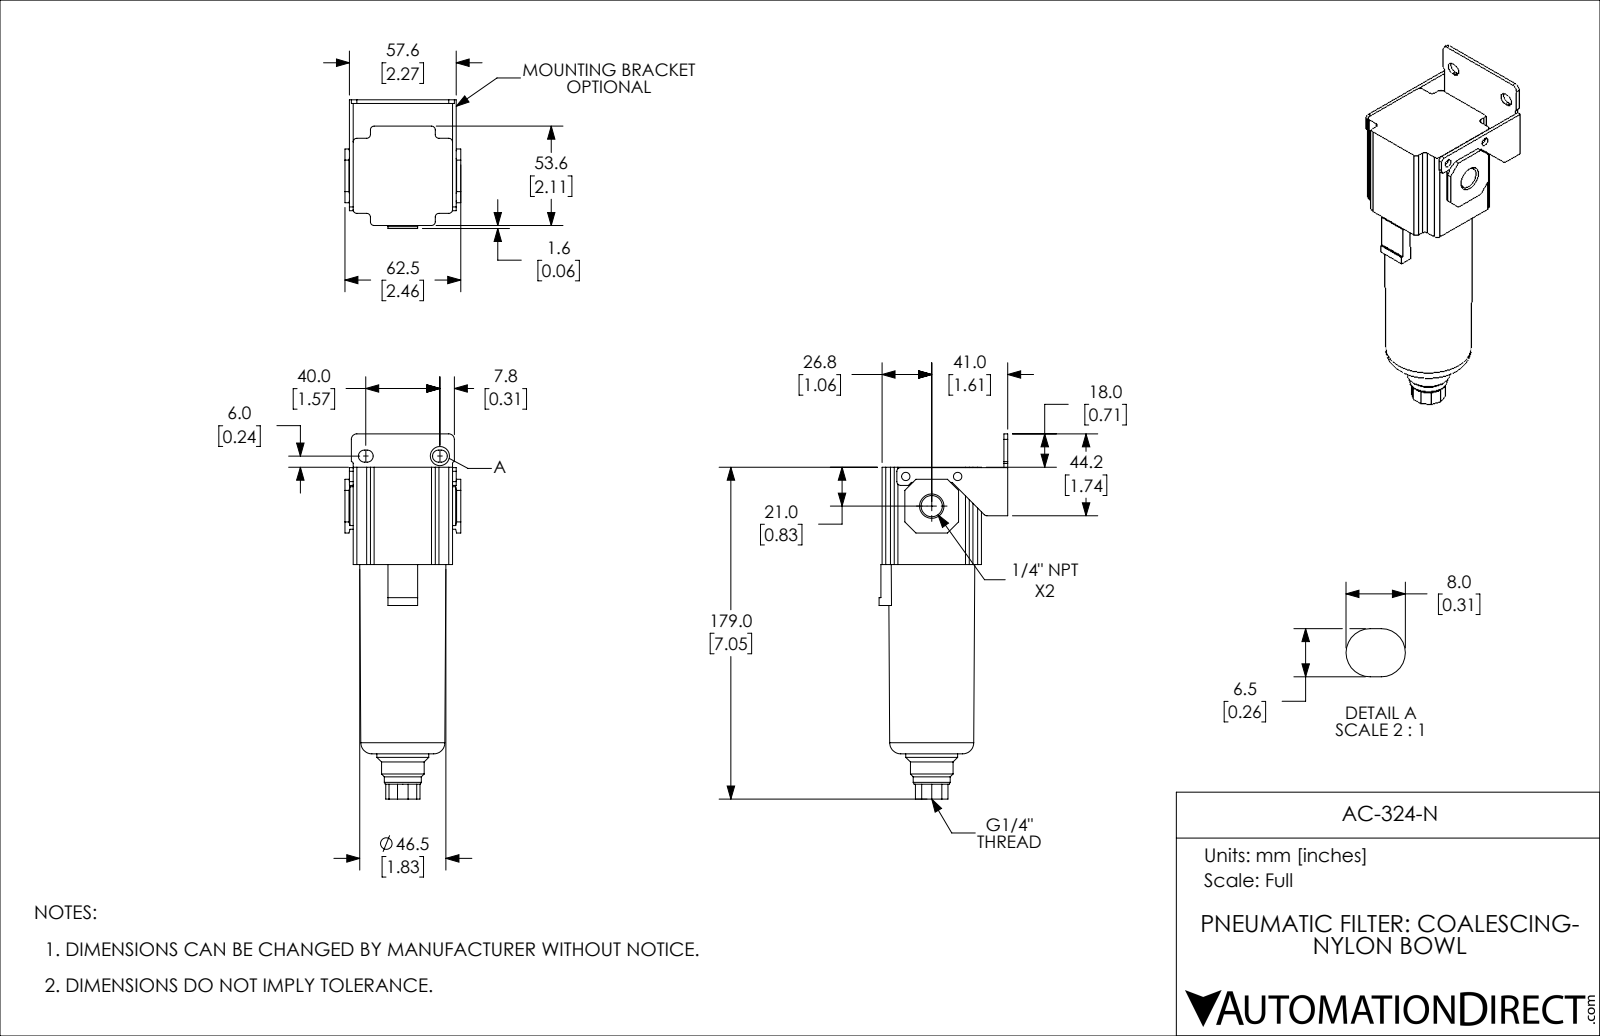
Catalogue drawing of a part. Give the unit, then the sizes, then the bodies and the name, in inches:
Units: inches
Overall size (bounding box): 7.756 × 2.733 × 2.461
Round holes (diameter × count): ⌀0.177 ×2, ⌀0.451 ×2
Round bosses / shafts (diameter × count): ⌀1.102 ×1, ⌀0.906 ×1, ⌀0.787 ×1
Partial cylindrical surfaces — rounded edges, fillets, slot ends (radius × count): R0.079 ×15, R0.128 ×4, R0.039 ×2, R0.118 ×2
Main face-to-face distances: 0.079, 2.11, 2.189, 0.559, 2.669, 0.48, 2.591, 0.096, 0.175, 2.285
Hole centre spacings: 0.837, 1.102
Volume: 20 in³ · Surface area: 65.25 in²
Bodies: 1 solid, 173 faces (109 planar, 48 cylindrical, 16 other)
Part name (STEP PRODUCT): AC-324-N
STEP written by: SolidWorks 2018 (AUTOMOTIVE_DESIGN)
